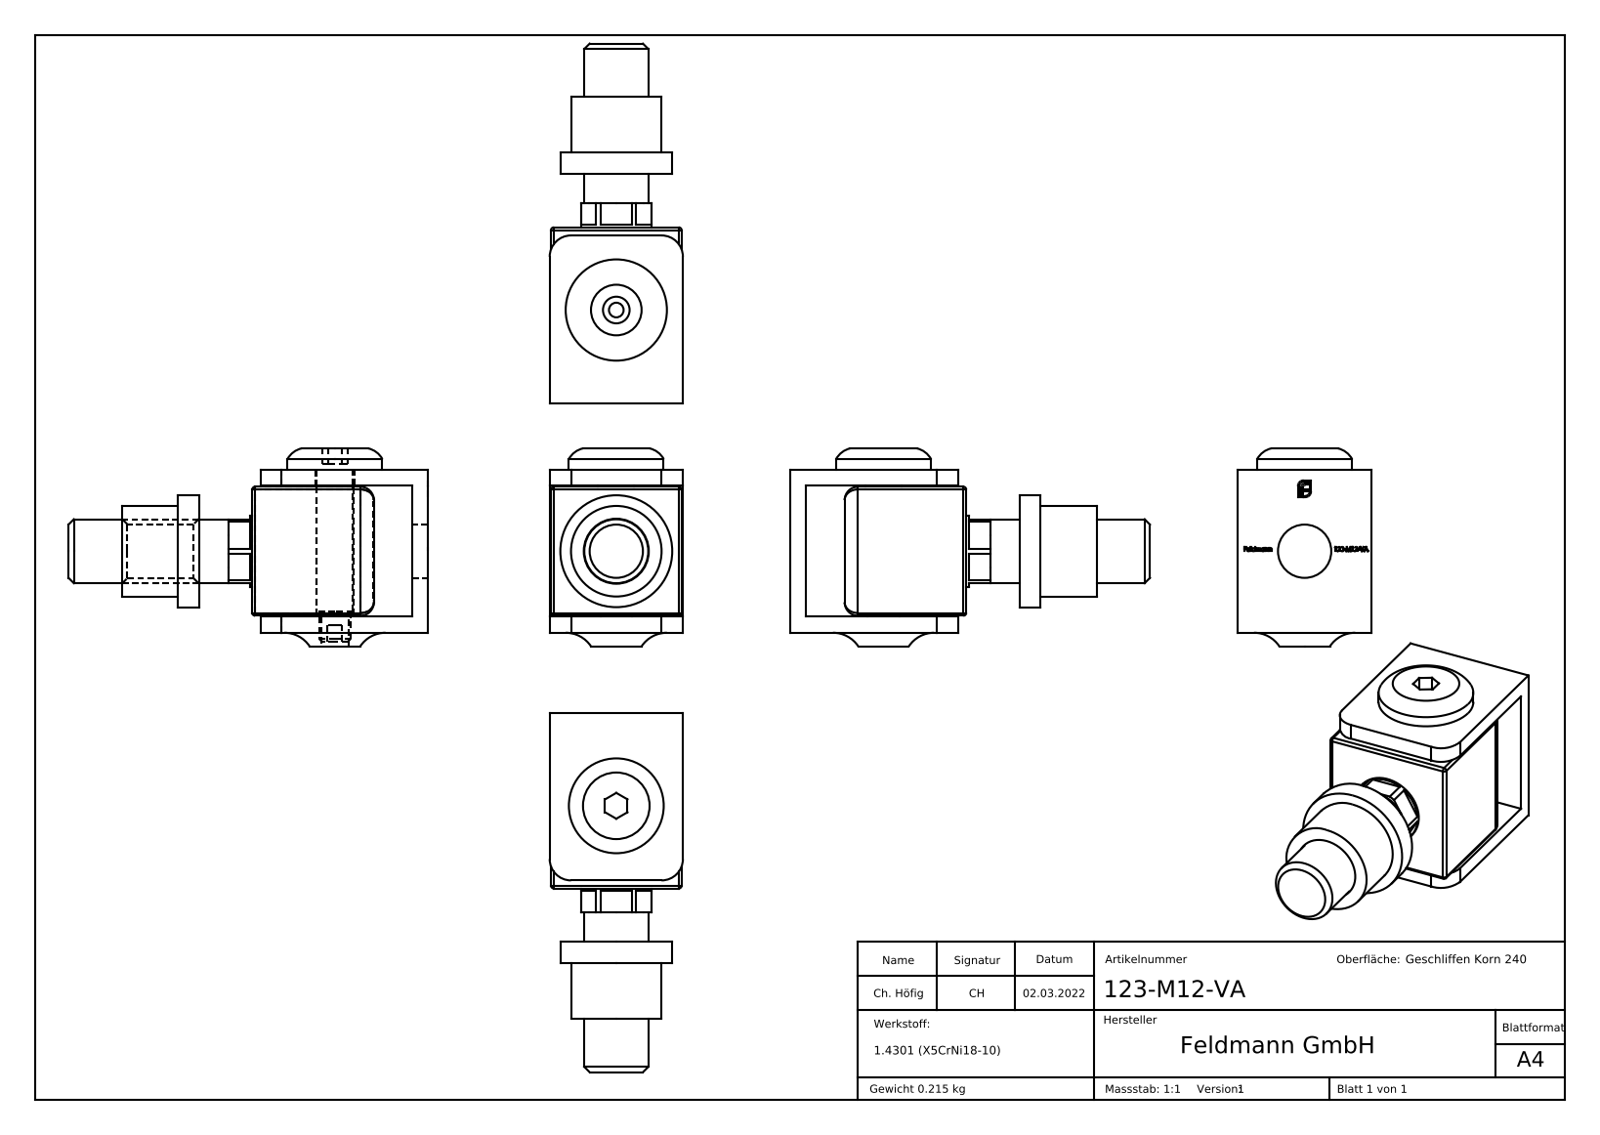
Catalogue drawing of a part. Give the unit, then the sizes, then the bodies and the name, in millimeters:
Units: millimetres
Overall size (bounding box): 67.5 × 37.15 × 25
Round holes (diameter × count): ⌀2.75 ×1, ⌀5 ×1, ⌀7 ×1, ⌀7.2 ×1, ⌀10 ×1, ⌀10.2 ×1
Round bosses / shafts (diameter × count): ⌀21 ×1, ⌀17.8 ×1, ⌀17 ×1, ⌀13.3 ×1, ⌀12 ×1, ⌀6.8 ×1, ⌀6 ×1
Partial cylindrical surfaces — rounded edges, fillets, slot ends (radius × count): R0.5 ×8, R2.5 ×4, R4 ×2
Main face-to-face distances: 3, 27.6, 3.2, 27.4, 24.4, 24.6, 24.5, 30.6, 24.75, 7.2
Volume: 27 275 mm³ · Surface area: 13 199 mm²
Bodies: 4 solids, 358 faces (219 planar, 29 cylindrical, 110 other)
Part name (STEP PRODUCT): 123-M12-VA; 123-MXX-VA Teil4_123-M12-VA Teil4; 123-MXX-VA Teil3_123-M12-VA Teil3; 123-MXX-VA Teil2_123-M12-VA Teil2 (+1 more)
STEP written by: SolidWorks 2018 (CONFIG_CONTROL_DESIGN)
